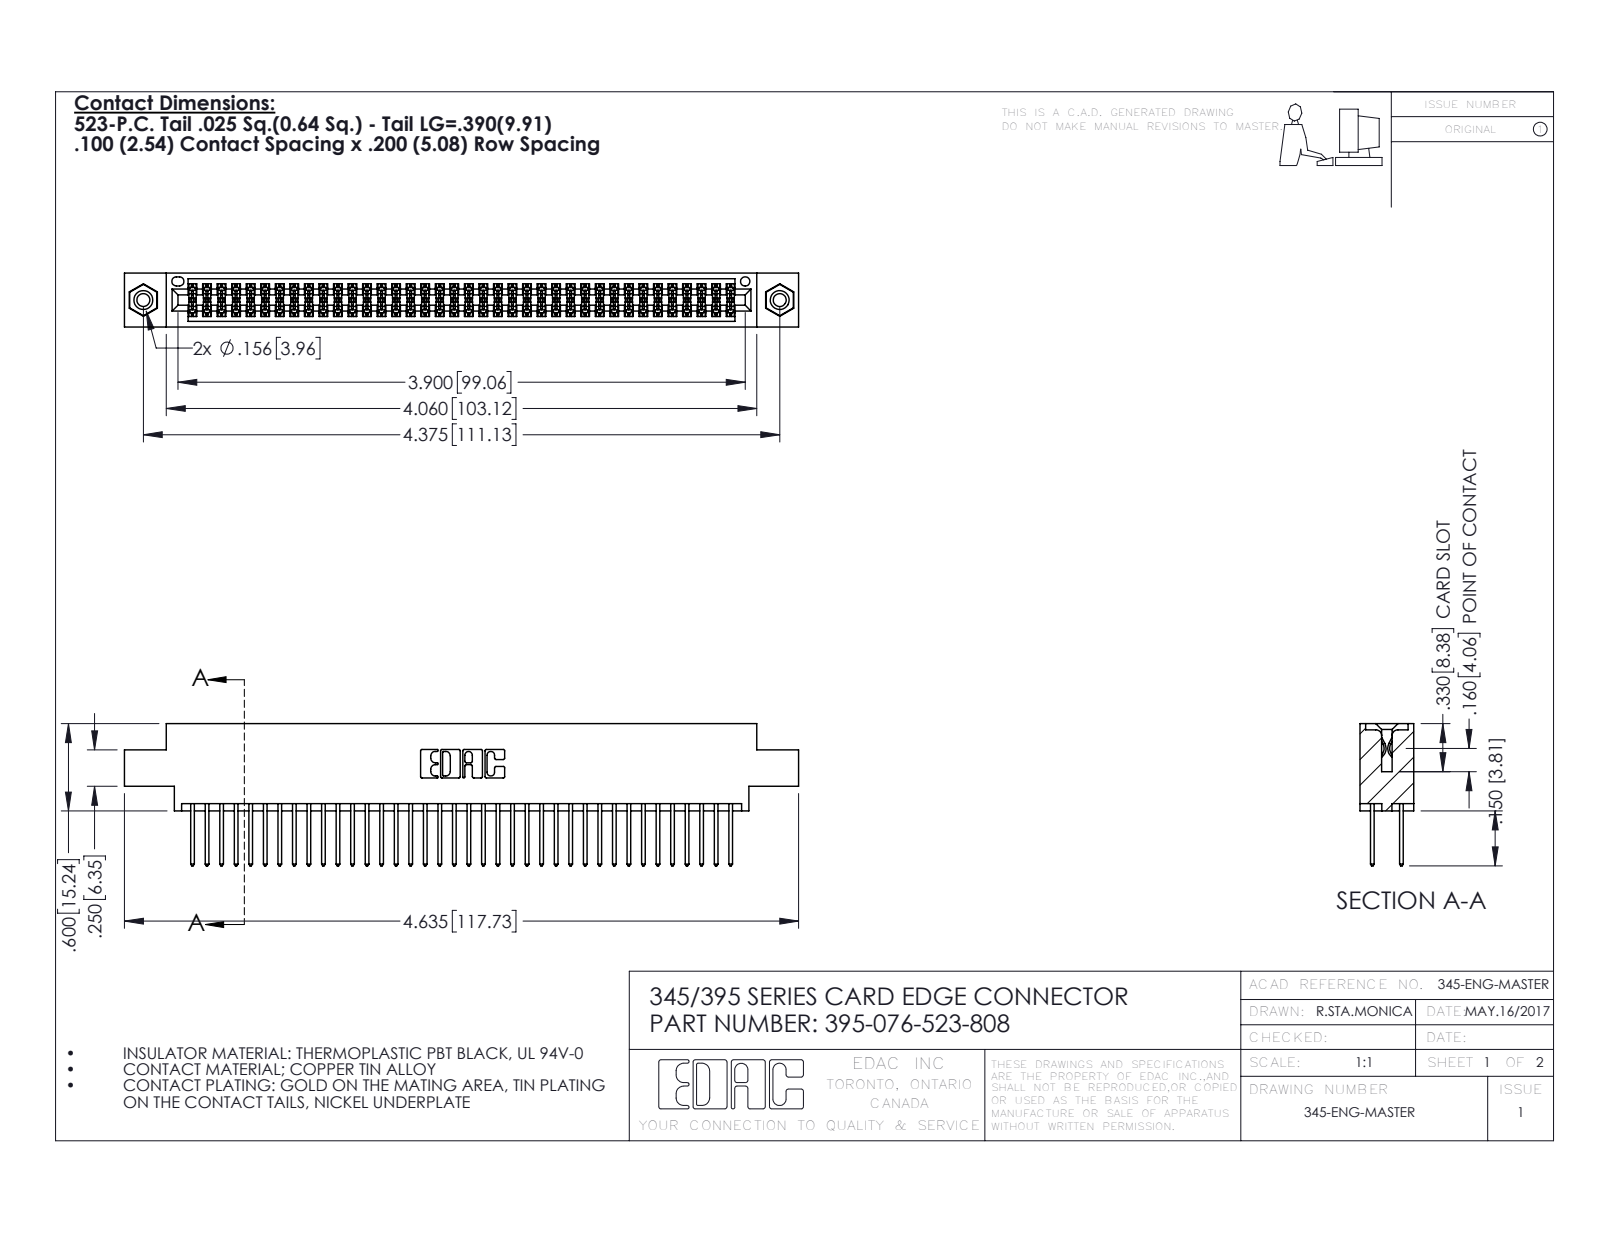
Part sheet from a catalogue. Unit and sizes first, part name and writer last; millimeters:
Units: millimetres
Overall size (bounding box): 117.7 × 24.8 × 9.4
Round holes (diameter × count): ⌀2.3 ×2, ⌀3.2 ×2, ⌀4 ×2, ⌀1.6 ×1
Round bosses / shafts (diameter × count): ⌀3.9 ×2
Partial cylindrical surfaces — rounded edges, fillets, slot ends (radius × count): R0.2 ×114, R0.3 ×76, R0.3 ×22, R0.2 ×6, R0.8 ×6, R0.7 ×3, R0.4 ×2, R0.5 ×2
Main face-to-face distances: 1.8, 7.6, 5.1, 2.5, 6.9, 0.6, 9.4, 5.7, 4.4, 3.8
Hole centre spacings: 6.9, 105.1, 111.1
Volume: 11 400 mm³ · Surface area: 17 680 mm²
Bodies: 79 solids, 3990 faces (2624 planar, 1350 cylindrical, 16 other)
Part name (STEP PRODUCT): 345-250-001_345-250-003-102; 345-292-001_345-293-123; 345 Part_0.170 Offset - 0.156 Dia-TI; 395-076-523-808
STEP written by: SolidWorks 2016 (CONFIG_CONTROL_DESIGN)
